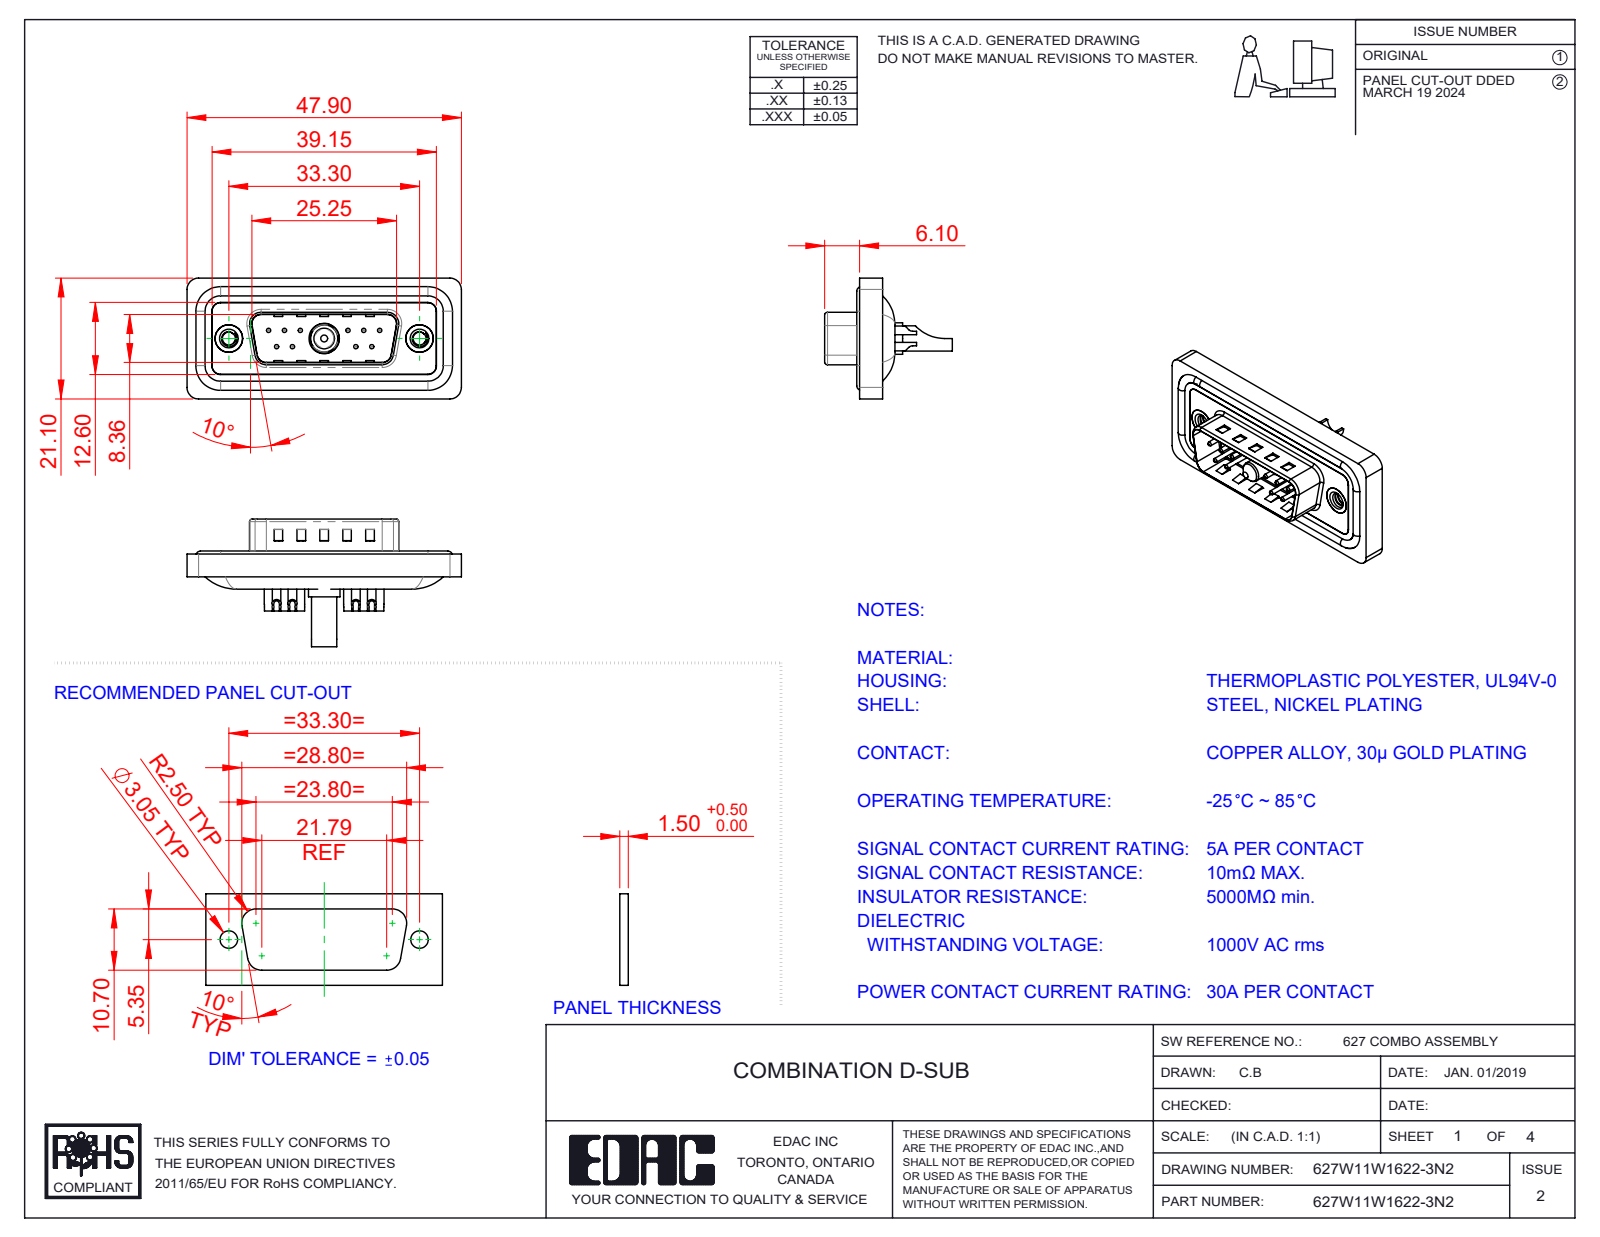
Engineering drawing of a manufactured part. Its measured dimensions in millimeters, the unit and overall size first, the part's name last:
Units: millimetres
Overall size (bounding box): 47.9 × 22.3 × 21.1
Round holes (diameter × count): ⌀0.75 ×10, ⌀1 ×10, ⌀1.6 ×10, ⌀2 ×10, ⌀2.26 ×2, ⌀4 ×2, ⌀4.8 ×2, ⌀5 ×2, ⌀3.5 ×1, ⌀4.85 ×1, ⌀5.3 ×1
Round bosses / shafts (diameter × count): ⌀1.5 ×10, ⌀1.6 ×4, ⌀4.9 ×2, ⌀5.5 ×1, ⌀5.2 ×1, ⌀4.75 ×1, ⌀4.4 ×1, ⌀3.75 ×1
Partial cylindrical surfaces — rounded edges, fillets, slot ends (radius × count): R1.5 ×26, R2 ×20, R1 ×9, R0.5 ×8, R1.6 ×8, R0.25 ×4, R0.6 ×4, R0.65 ×4
Main face-to-face distances: 0.4, 1.1, 1.6, 1.5, 0.5, 2.9, 3.1, 2.5, 4.1, 0.82
Hole centre spacings: 3.16, 2.77, 13.85, 11.08, 16.62, 5.03, 5.04, 5.54
Volume: 5 487 mm³ · Surface area: 9 023 mm²
Bodies: 19 solids, 875 faces (289 planar, 370 cylindrical, 216 other)
Part name (STEP PRODUCT): 627Combo Contact Row 1_22; Power Pin_30A SC; 627Combo Housing_11W1; 627Combo Shell Front_15 Contacts (+5 more)
STEP written by: SolidWorks 2023 (CONFIG_CONTROL_DESIGN)
